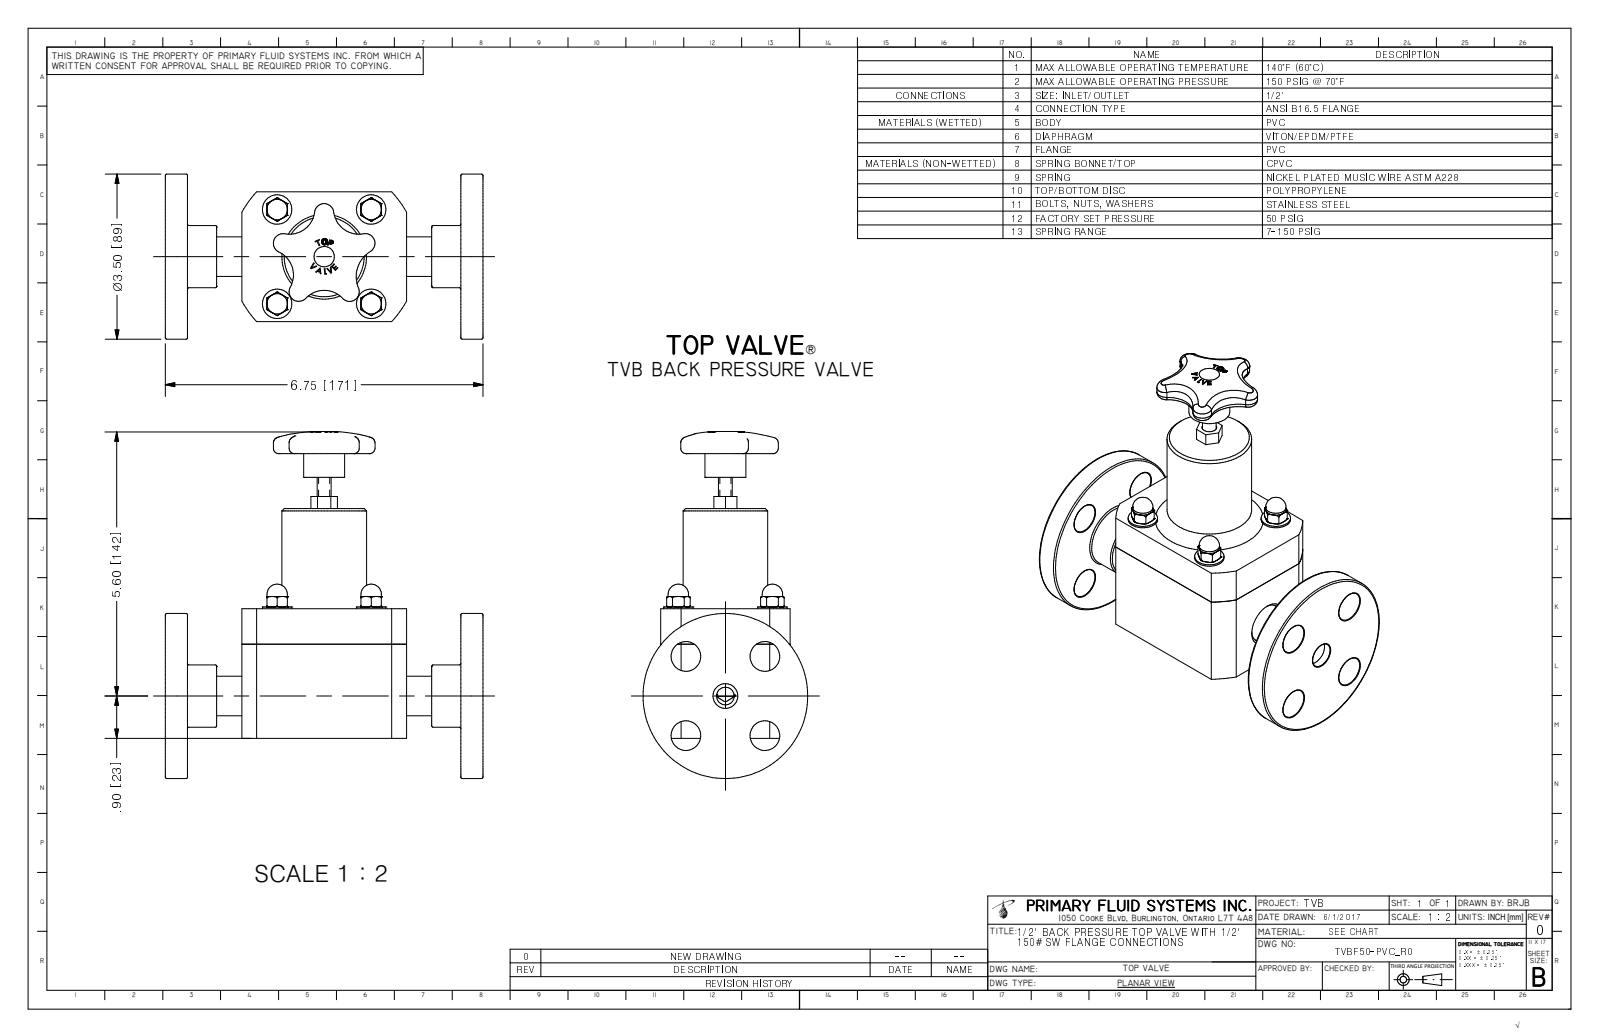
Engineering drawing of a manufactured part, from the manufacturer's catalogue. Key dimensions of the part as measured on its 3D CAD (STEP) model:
Part name (STEP PRODUCT): TVBF50-PVC_R0
STEP written by: Autodesk Inventor 2009 (AUTOMOTIVE_DESIGN)
Units: inches
Bodies: 1 solid, 393 faces (152 planar, 57 cylindrical, 184 other)
Overall size (bounding box): 7.362 × 6.75 × 3.5
Volume: 41.77 in³ · Surface area: 153.6 in²
Round holes (diameter × count): ⌀0.175 ×4, ⌀0.63 ×4, ⌀0.526 ×1
Round bosses / shafts (diameter × count): ⌀0.625 ×4, ⌀0.433 ×4, ⌀0.375 ×4, ⌀3.5 ×1, ⌀1.8 ×1, ⌀1.32 ×1, ⌀0.87 ×1, ⌀0.293 ×1
Partial cylindrical surfaces — rounded edges, fillets, slot ends (radius × count): R0.085 ×5, R0.205 ×5, R0.536 ×4, R0.656 ×4, R0.625 ×1, R0.745 ×1, R1.988 ×1
Main face-to-face distances: 0.47, 6.28, 1.625, 5.125, 1.155, 4.655, 2.75, 6.75, 5.81, 3.5
Hole centre spacings: 1.188, 1.68, 2, 2.375, 2.828
